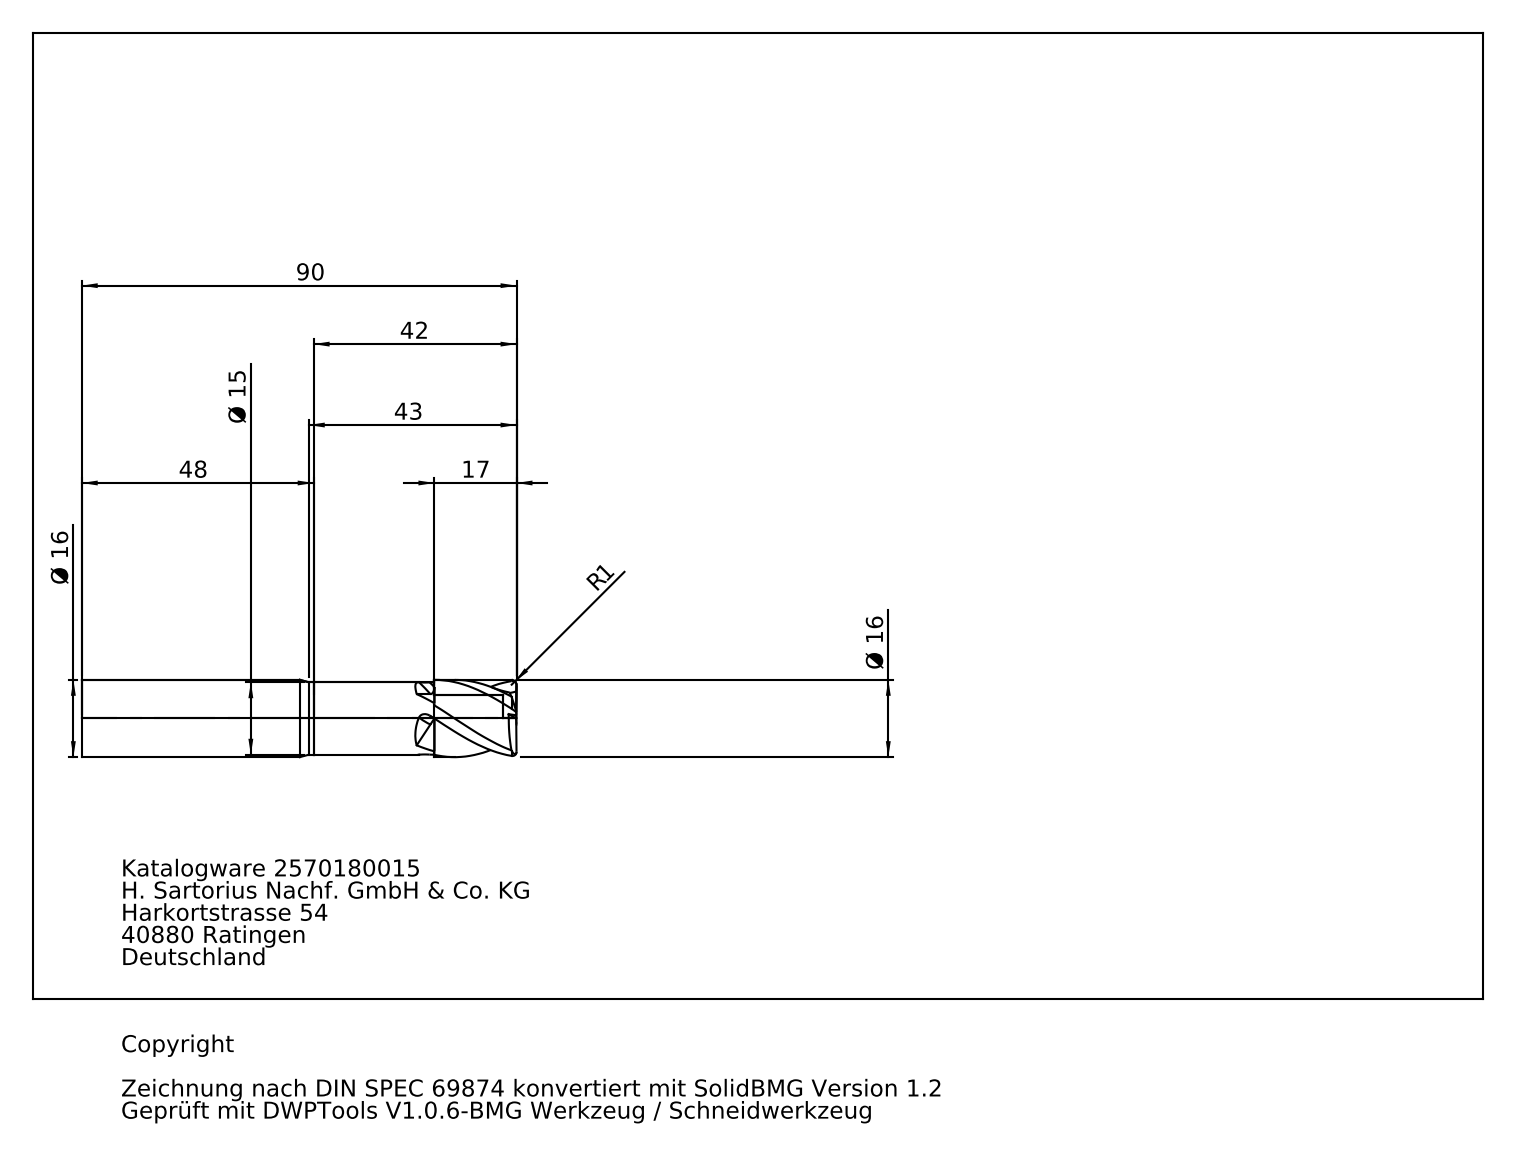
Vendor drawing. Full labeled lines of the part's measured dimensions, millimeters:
Part name (STEP PRODUCT): 2570180015
STEP written by: SolidWorks 2010 (AUTOMOTIVE_DESIGN)
Units: millimetres
Bodies: 2 solids, 59 faces (14 planar, 17 cylindrical, 28 other)
Overall size (bounding box): 90 × 16 × 16
Volume: 16 100 mm³ · Surface area: 5 972 mm²
Round holes (diameter × count): ⌀9.6 ×1
Round bosses / shafts (diameter × count): ⌀16 ×1, ⌀15 ×1
Main face-to-face distances: 87.28, 73, 14.28, 89.94, 16.94, 2.66
